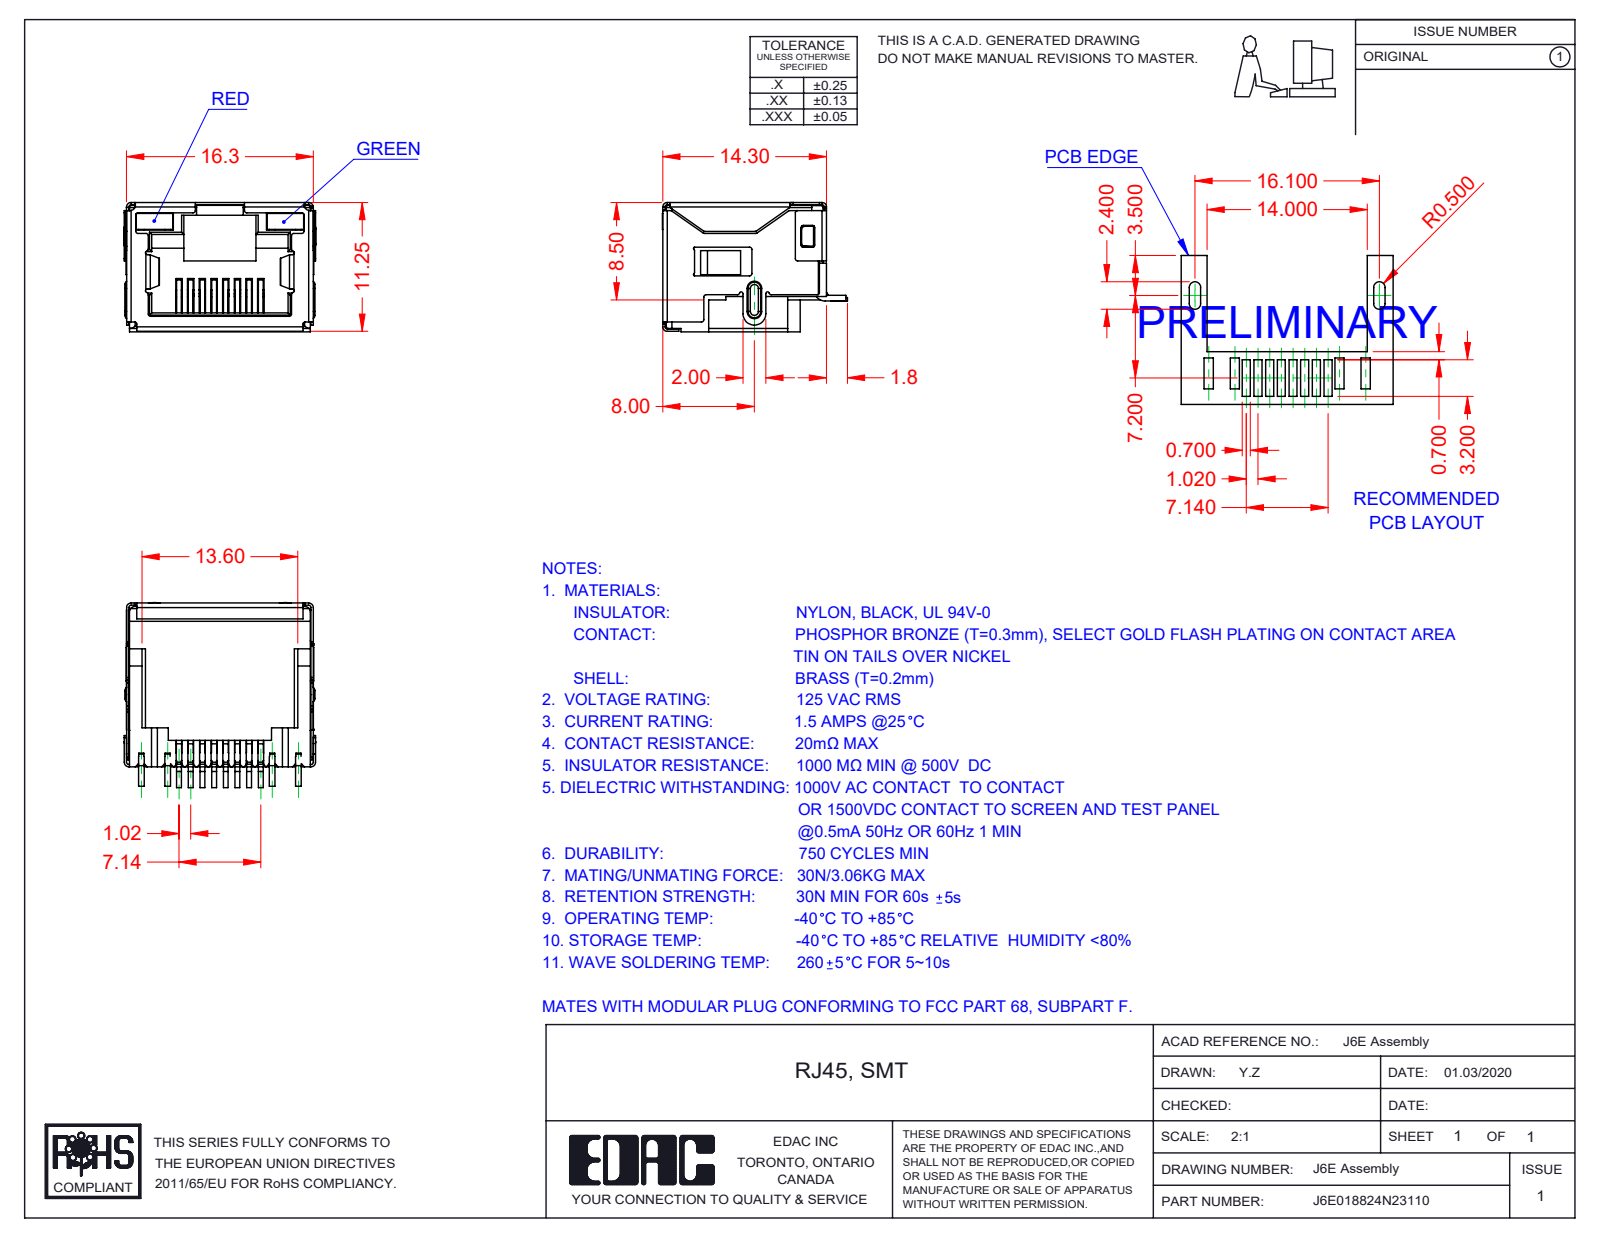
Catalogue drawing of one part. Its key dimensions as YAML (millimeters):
part_name: "6E Shield_LED; 6E LED LH_2-Red; 6E LED RH_3-Green; 6E Insulator_LED (+2 more)"
step_written_by: "SolidWorks 2016 (CONFIG_CONTROL_DESIGN)"
units: millimeters
bodies: {solids: 12, faces: 1496, planar: 1099, cylindrical: 347, other: 50}
overall_size: [16.75, 16.15, 11.3]
volume: 1109
surface_area: 4045
partial_cylinders:
  - {radius: 0.2, count: 82}
  - {radius: 0.25, count: 17}
  - {radius: 0.4, count: 13}
  - {radius: 0.5, count: 13}
  - {radius: 0.1, count: 10}
  - {radius: 0.15, count: 7}
  - {radius: 0.3, count: 4}
  - {radius: 1, count: 3}
face_to_face_distances: [11.05, 16.05, 16.1, 15.85, 11.1, 11.3, 2.4, 0.7, 9.85, 0.49]
